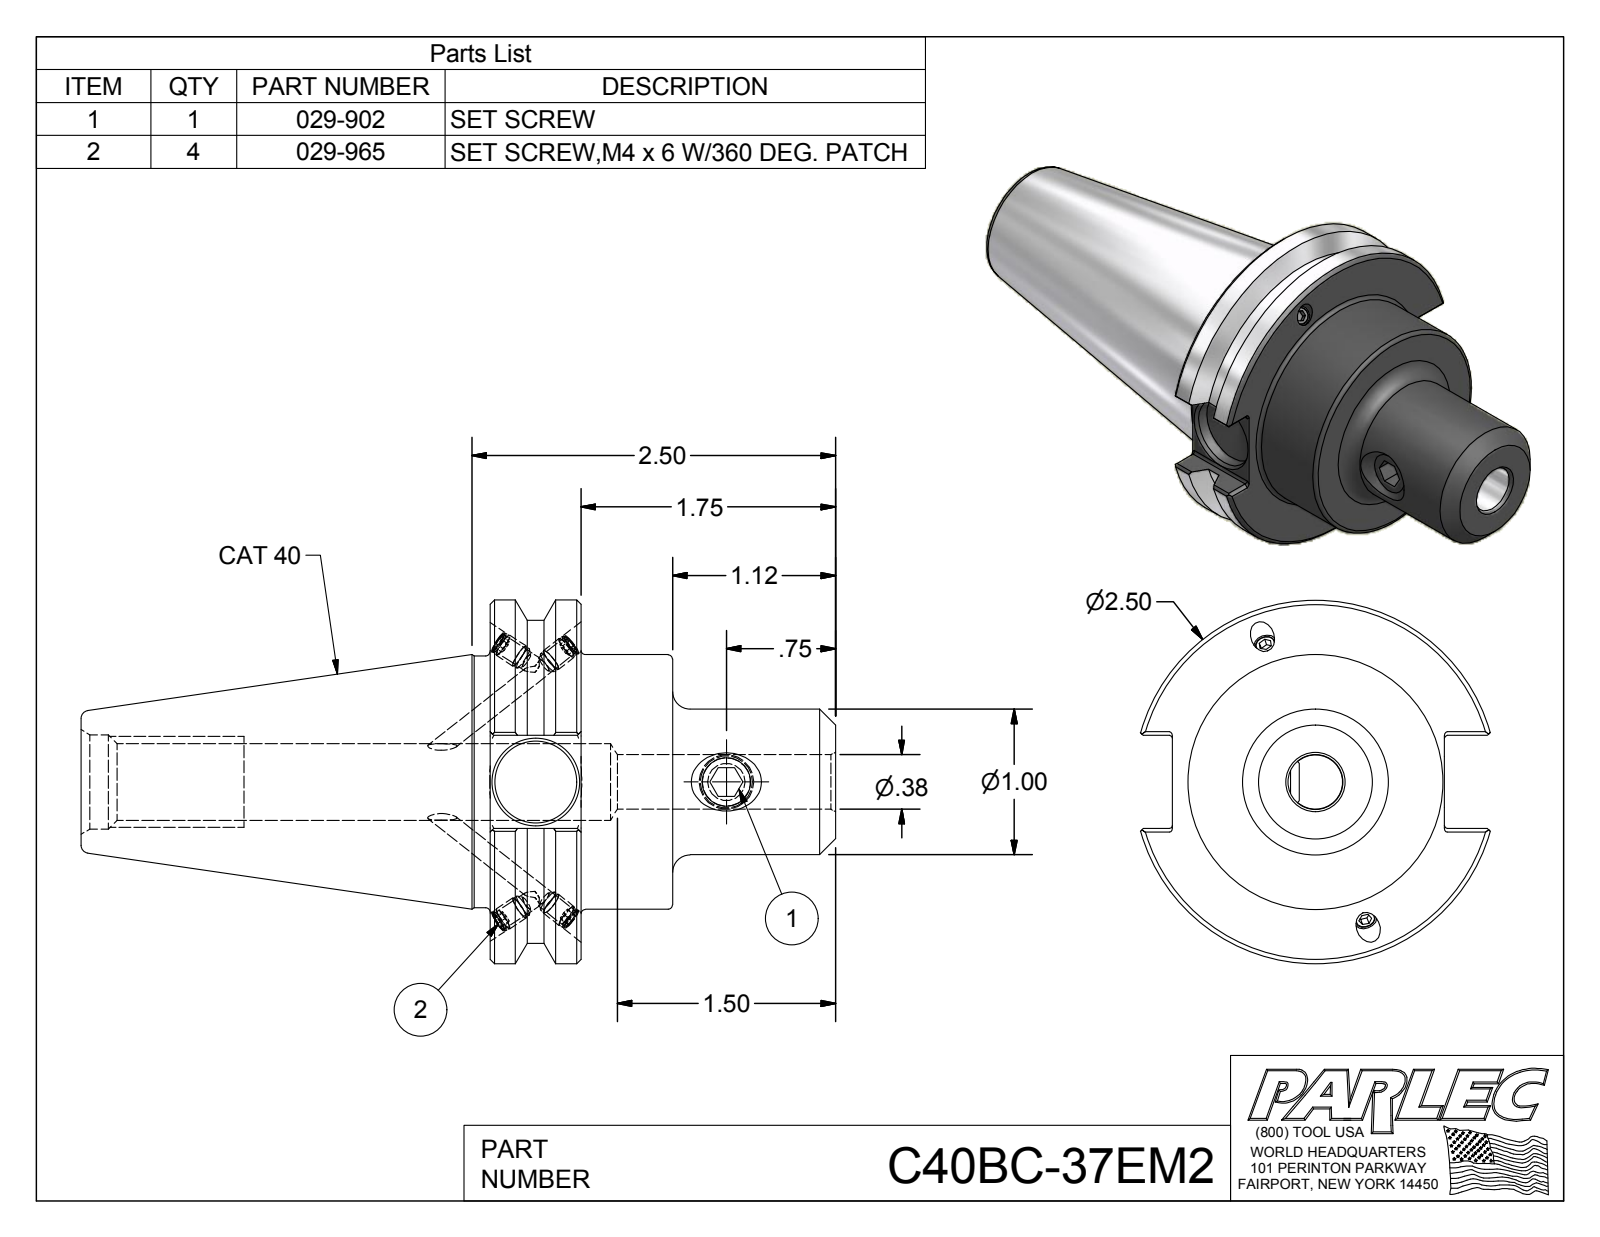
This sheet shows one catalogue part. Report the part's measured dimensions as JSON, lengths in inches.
{"part_name": "C40BC-37EM2; C40BC-37EM2-1; 029-902; 029-965", "step_written_by": "Autodesk Inventor 2012 (AUTOMOTIVE_DESIGN)", "units": "inches", "bodies": {"solids": 6, "faces": 182, "planar": 85, "cylindrical": 48, "other": 49}, "overall_size": [5.187, 2.5, 2.406], "volume_in3": 8.26, "surface_area_in2": 42.78, "round_holes": [[0.13, 4], [0.161, 4], [0.315, 1], [0.33, 1], [0.375, 1], [0.399, 1], [0.527, 1], [0.648, 1]], "round_bosses_or_shafts": [[0.165, 4], [0.157, 4], [2.5, 1], [2.219, 1], [1.75, 1], [1.73, 1], [1, 1], [0.375, 1]], "partial_cylinders_radius": [[0.02, 12]], "face_to_face_distances": [0.625, 1.255, 0.63, 2.375, 1.75, 1.12, 0.64, 0.236, 1.86, 2.812], "hole_center_spacings": [1.31]}
